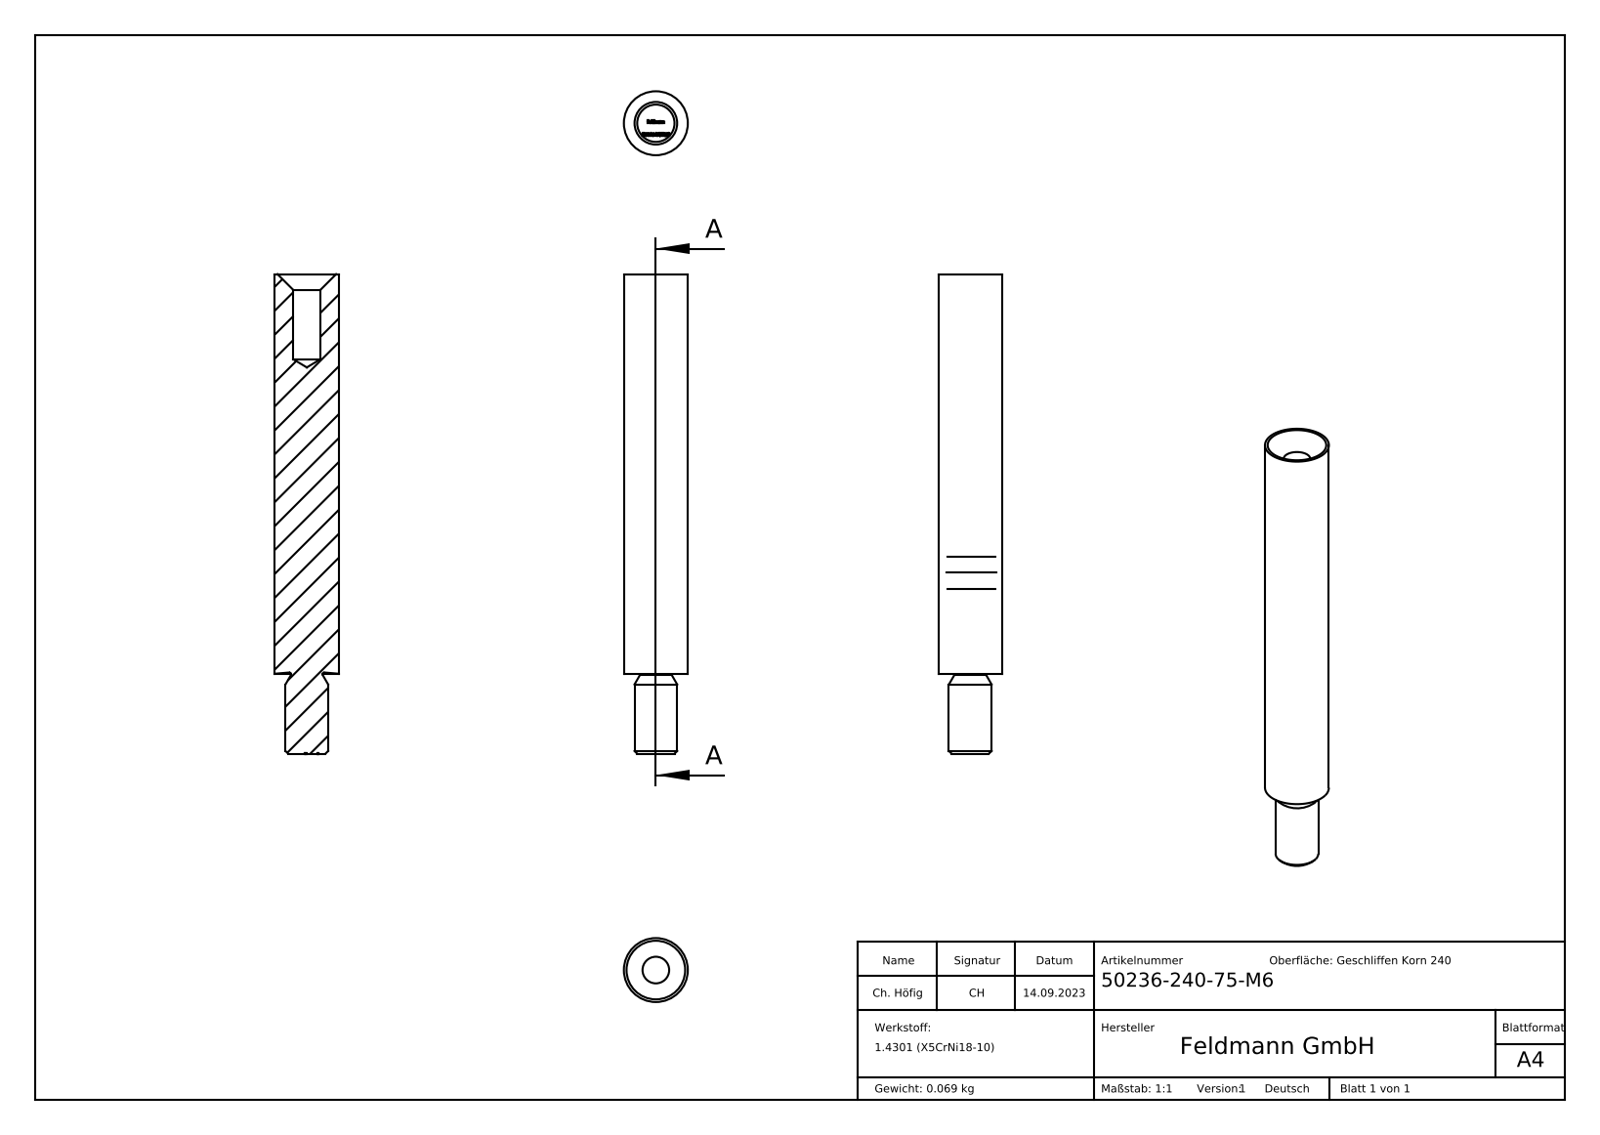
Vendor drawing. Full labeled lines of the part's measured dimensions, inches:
Part name (STEP PRODUCT): 50236-240-75-M6
STEP written by: SolidWorks 2018 (CONFIG_CONTROL_DESIGN)
Units: inches
Bodies: 1 solid, 269 faces (157 planar, 3 cylindrical, 109 other)
Overall size (bounding box): 3.543 × 0.472 × 0.472
Volume: 0.535 in³ · Surface area: 5.72 in²
Round holes (diameter × count): ⌀0.197 ×1
Round bosses / shafts (diameter × count): ⌀0.472 ×1, ⌀0.315 ×1
Main face-to-face distances: 3.543, 3.539, 0.03, 0.051, 0.094, 0.094, 0.028, 0.061, 0.096, 0.022
